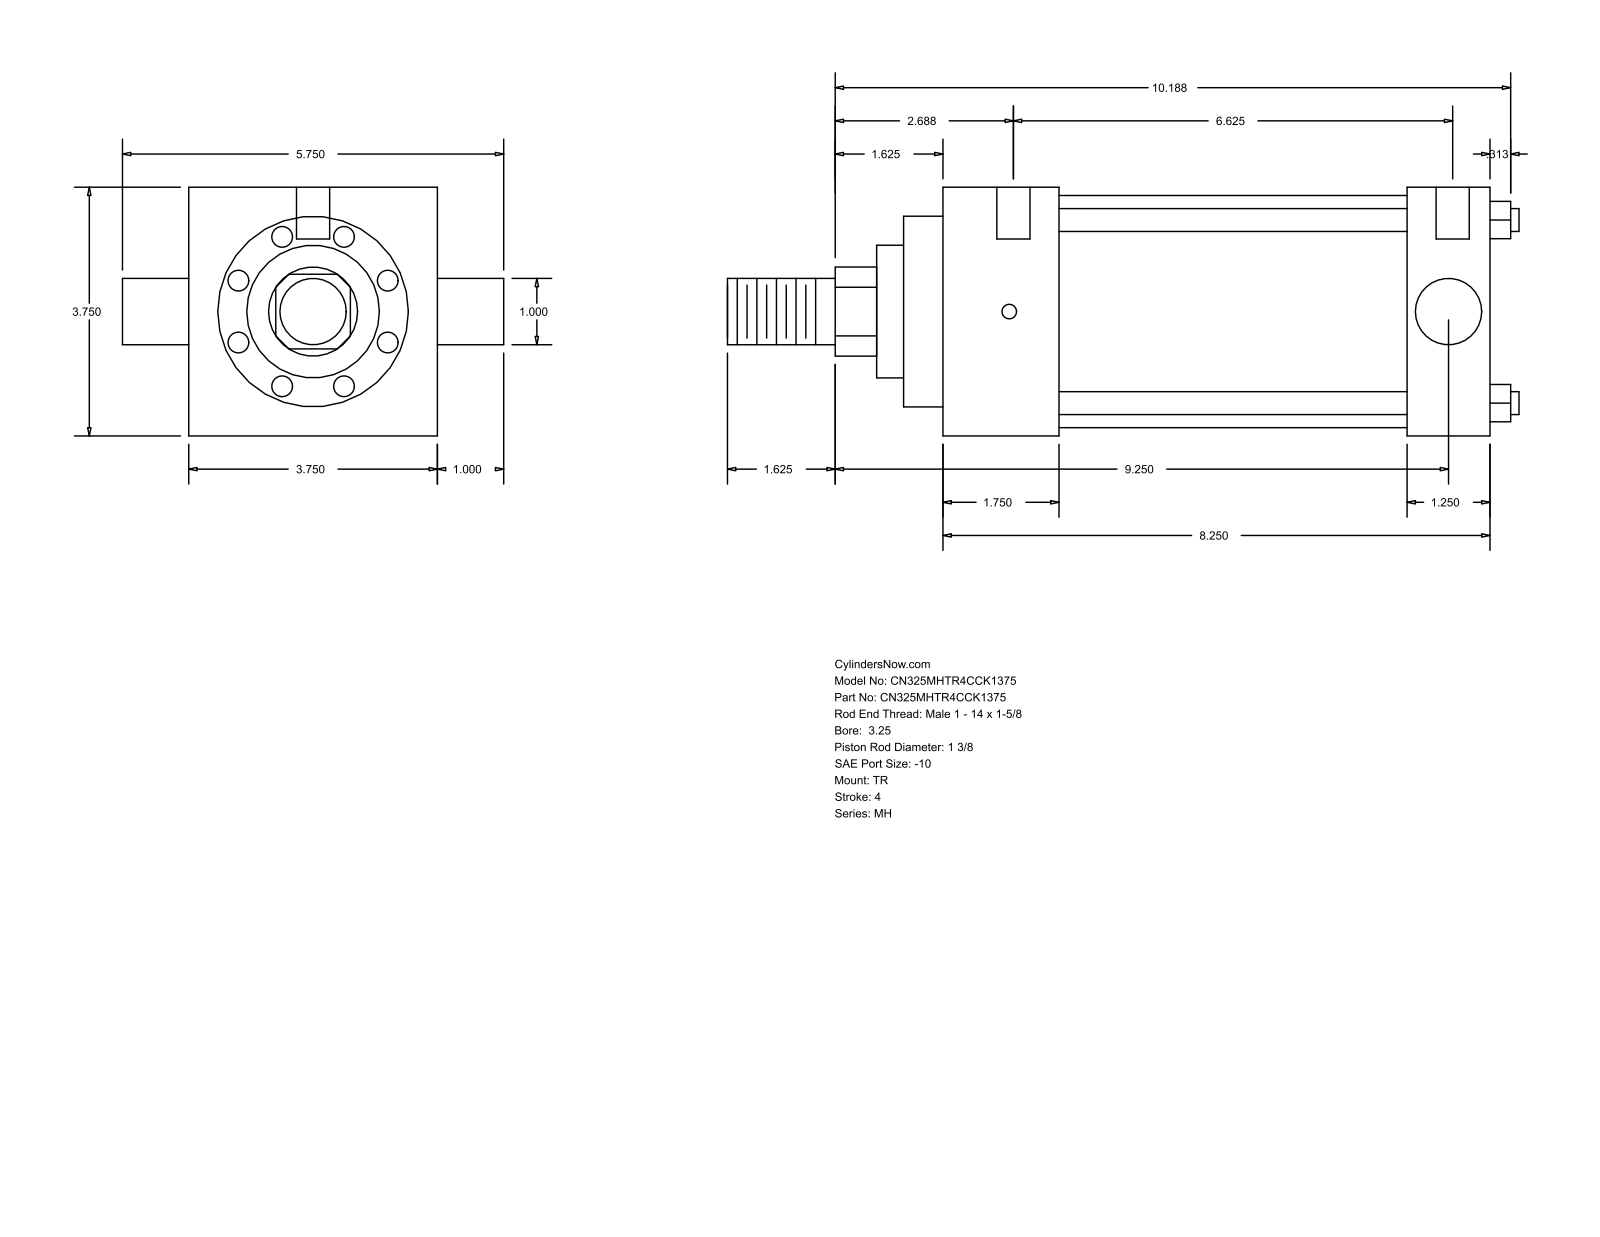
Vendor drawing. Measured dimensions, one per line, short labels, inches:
name: MH_TR__0325_1.375
written by: GSSL Pune (CONFIG_CONTROL_DESIGN)
unit: in
bodies: 0 solids, 86 faces (61 planar, 25 cylindrical, 0 other)
size: 11.937 × 5.75 × 3.75
holes: 3× ⌀0.219, 2× ⌀0.5
bosses: 4× ⌀0.345, 2× ⌀1, 1× ⌀3.5, 1× ⌀2.875, 1× ⌀2, 1× ⌀1.375
rounds: 1× R0.672
face distances: 3.75, 8.25, 1.75, 7, 5.25, 6.5, 1.25, 0.594, 2.344, 7.594
hole spacings: 0.063, 0.187, 6.625, 6.688, 6.813, 6.875
